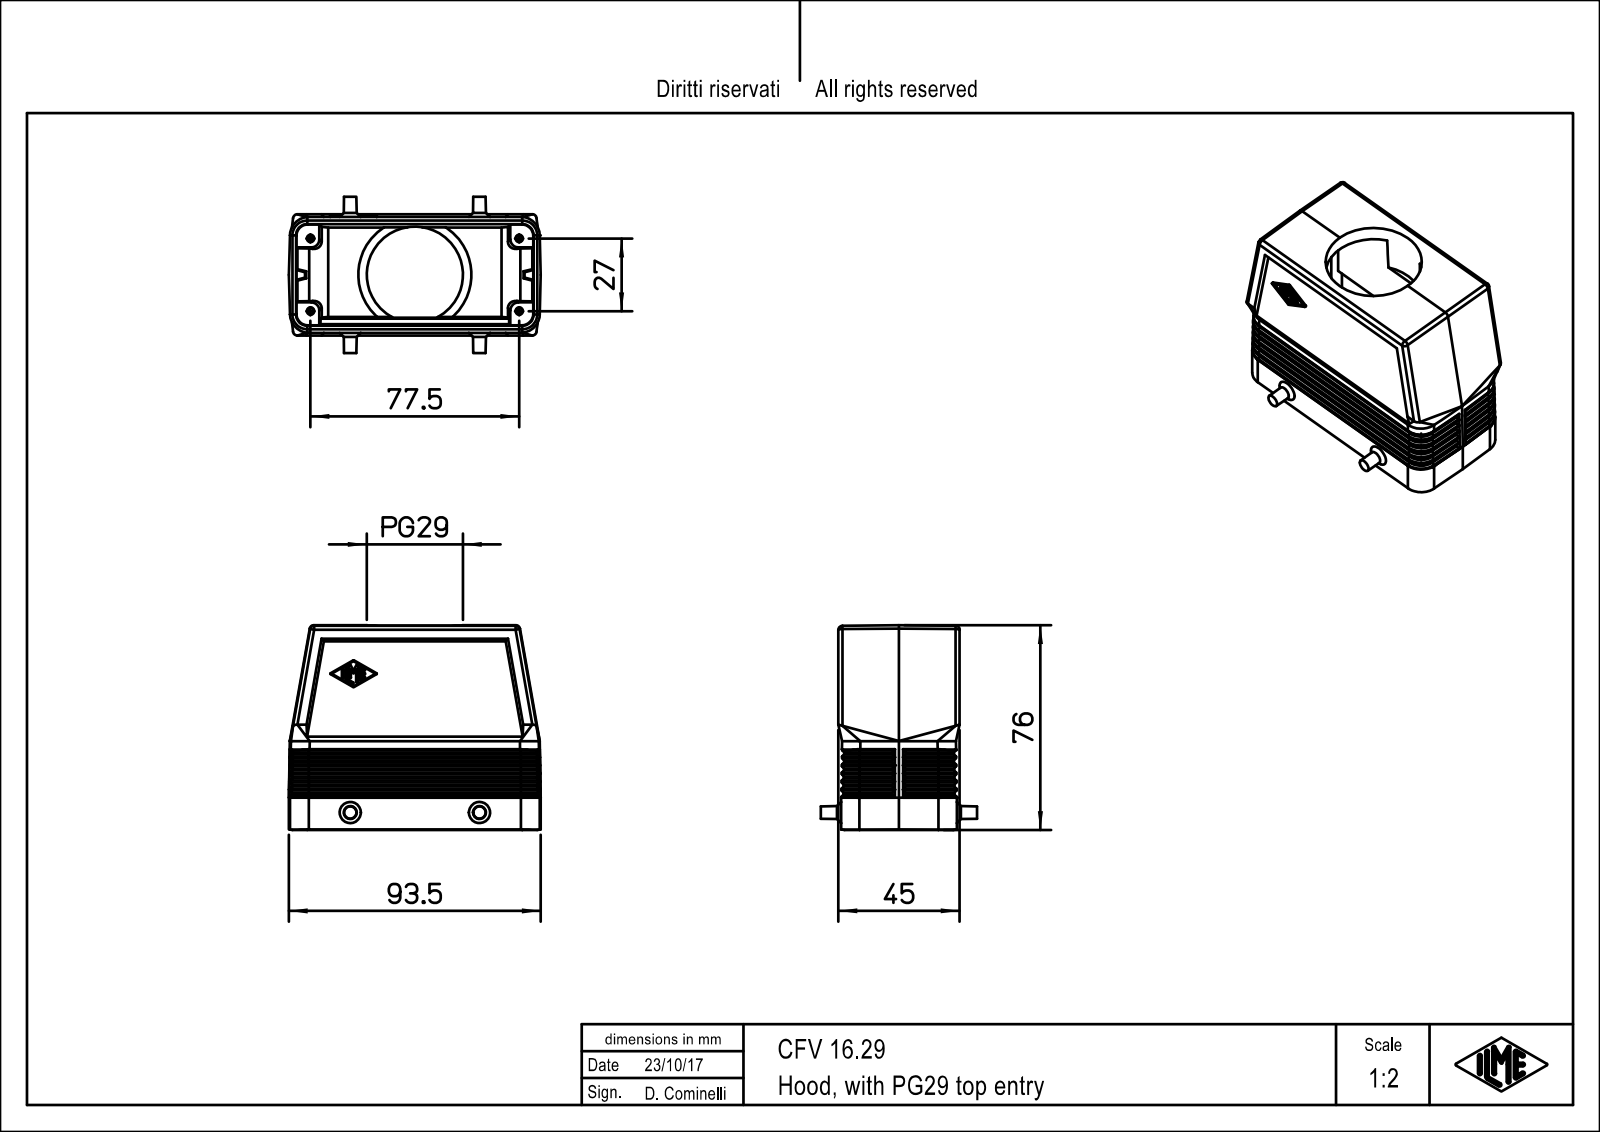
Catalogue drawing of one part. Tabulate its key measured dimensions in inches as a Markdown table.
| quantity | value |
| --- | --- |
| part name | CFV_16.29 |
| STEP written by | PTC Creo Elements/Direct Modeling 19.0E 27-Jun-2016 (C) Parametric Technology GmbH (AUTOMOTIVE_DESIGN) |
| units | inches |
| bodies | 1 solid, 527 faces (240 planar, 135 cylindrical, 152 other) |
| overall size | 3.681 × 2.992 × 2.283 |
| volume | 5.347 in³ |
| surface area | 67.21 in² |
| round holes (diameter × count) | 1.406 × 1 |
| partial cylindrical surfaces (radius × count) | 0.02 × 78, 0.013 × 15, 0.059 × 10, 0.276 × 8, 0.118 × 4, 0.165 × 4, 0.007 × 3, 0.026 × 1 |
| main face-to-face distances | 1.693, 0.079, 0.079, 0.335, 0.157, 1.732, 0.039, 0.236, 0.237, 0.158 |
